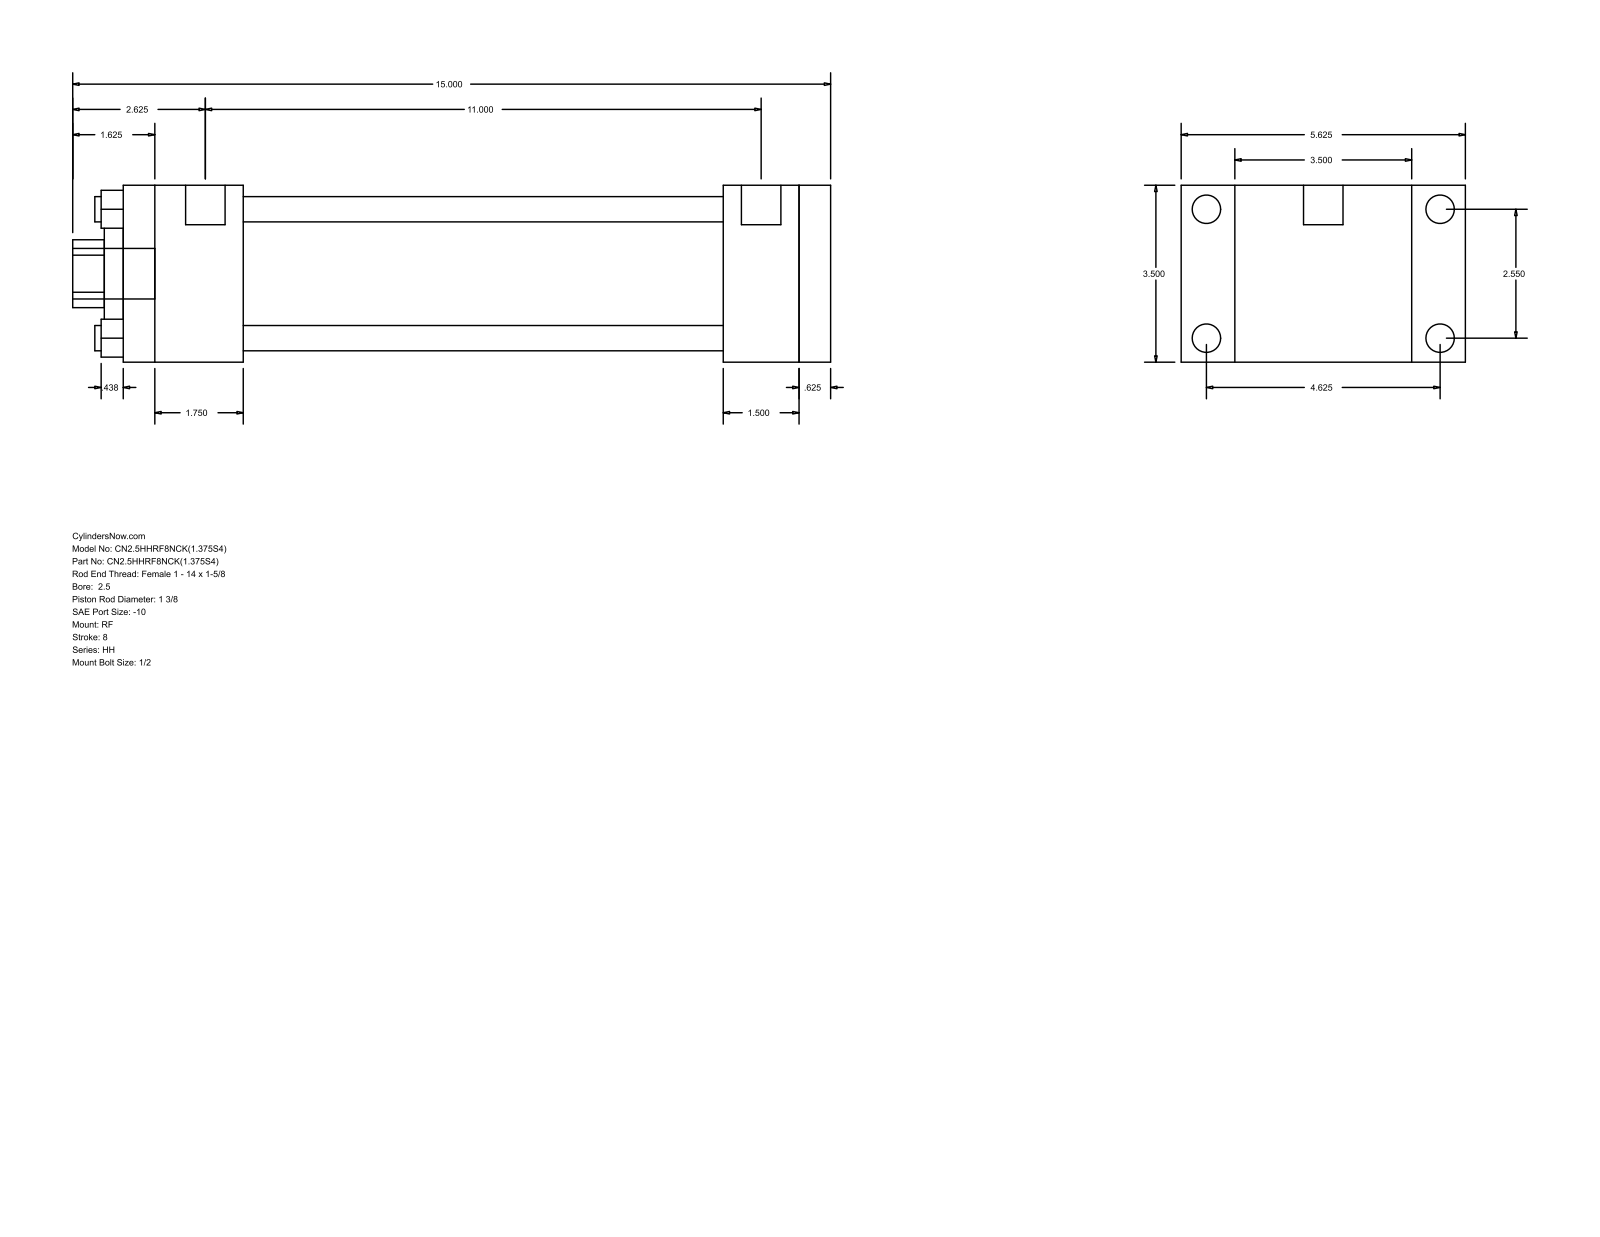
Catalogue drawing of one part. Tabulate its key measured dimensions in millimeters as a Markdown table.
| quantity | value |
| --- | --- |
| part name | HH_RF__0250_1.375 |
| STEP written by | GSSL Pune (CONFIG_CONTROL_DESIGN) |
| units | millimeters |
| bodies | 0 solids, 92 faces (64 planar, 28 cylindrical, 0 other) |
| overall size | 381 × 142.88 × 88.9 |
| round holes (diameter × count) | 12.7 × 4, 34.92 × 1, 50.8 × 1, 73.03 × 1 |
| round bosses / shafts (diameter × count) | 14.3 × 4, 5.56 × 4, 19.84 × 2, 25.4 × 1 |
| partial cylindrical surfaces (radius × count) | 17.06 × 1 |
| main face-to-face distances | 88.9, 355.6, 15.88, 339.72, 60.32, 279.4, 295.28, 301.62, 241.3, 38.1 |
| hole center spacings | 45.79, 64.76, 91.58 |
